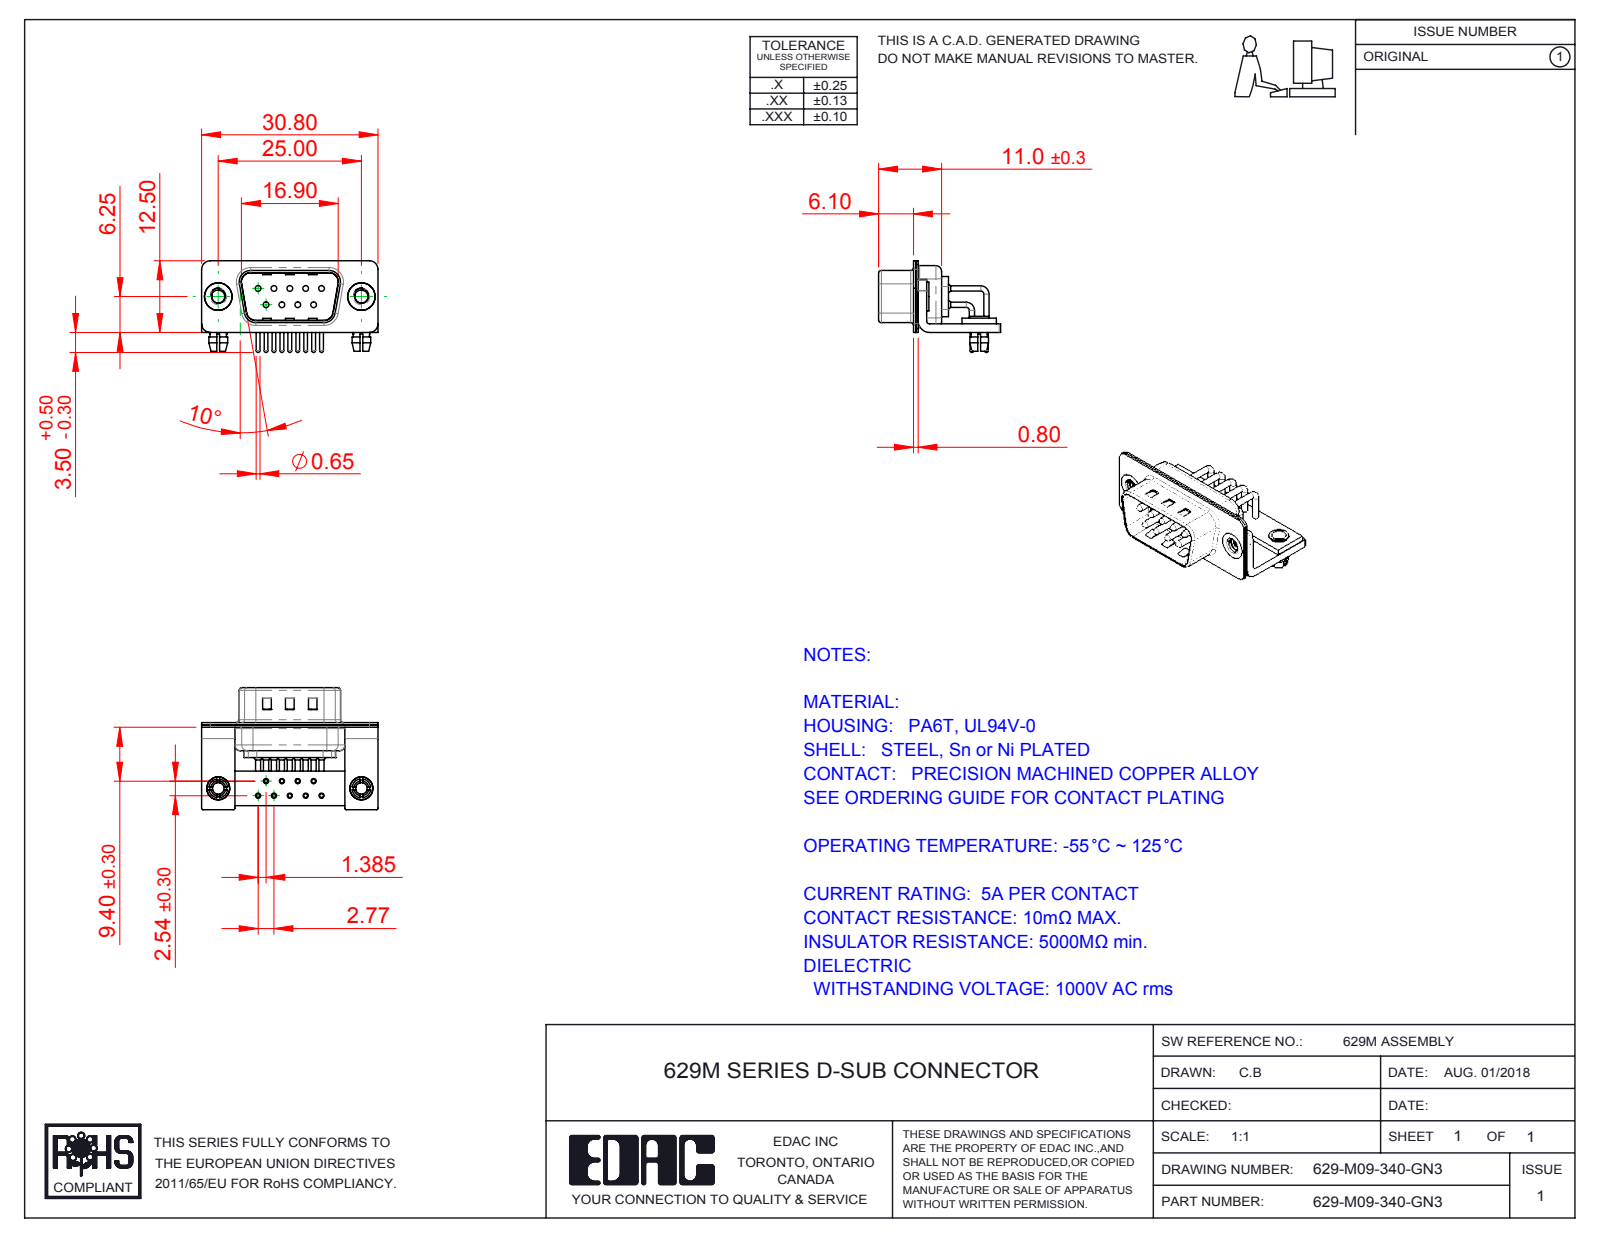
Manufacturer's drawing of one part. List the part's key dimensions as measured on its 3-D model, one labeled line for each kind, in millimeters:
Part name (STEP PRODUCT): 629M Stabilizer Board_09 Contacts; 629M 4-40 Threaded Rivet_Stabilizer; 629M Shell Front_09 Contacts; 629M Housing_09 Contacts (+6 more)
STEP written by: SolidWorks 2016 (CONFIG_CONTROL_DESIGN)
Units: millimetres
Bodies: 19 solids, 1454 faces (757 planar, 525 cylindrical, 172 other)
Overall size (bounding box): 30.8 × 21.3 × 16
Volume: 1 856 mm³ · Surface area: 5 184 mm²
Round holes (diameter × count): ⌀2 ×11, ⌀0.9 ×9, ⌀1 ×9, ⌀1.7 ×9, ⌀2.26 ×2, ⌀2.5 ×2, ⌀3.2 ×2, ⌀4 ×2, ⌀4.8 ×2
Round bosses / shafts (diameter × count): ⌀1.5 ×9, ⌀0.9 ×9, ⌀0.65 ×9, ⌀5 ×2, ⌀4.9 ×2, ⌀4 ×2, ⌀3.4 ×2, ⌀3.3 ×2
Partial cylindrical surfaces — rounded edges, fillets, slot ends (radius × count): R0.25 ×16, R1.5 ×16, R2 ×13, R0.5 ×9, R1.01 ×9, R1.6 ×8, R0.6 ×4, R0.65 ×4
Main face-to-face distances: 0.4, 1.5, 0.8, 0.85, 1.25, 1.9, 1, 2.5, 10.4, 9.55
Hole centre spacings: 2.77, 5.54, 3.16, 4.87, 8.31, 2.89, 2.9, 5.03
